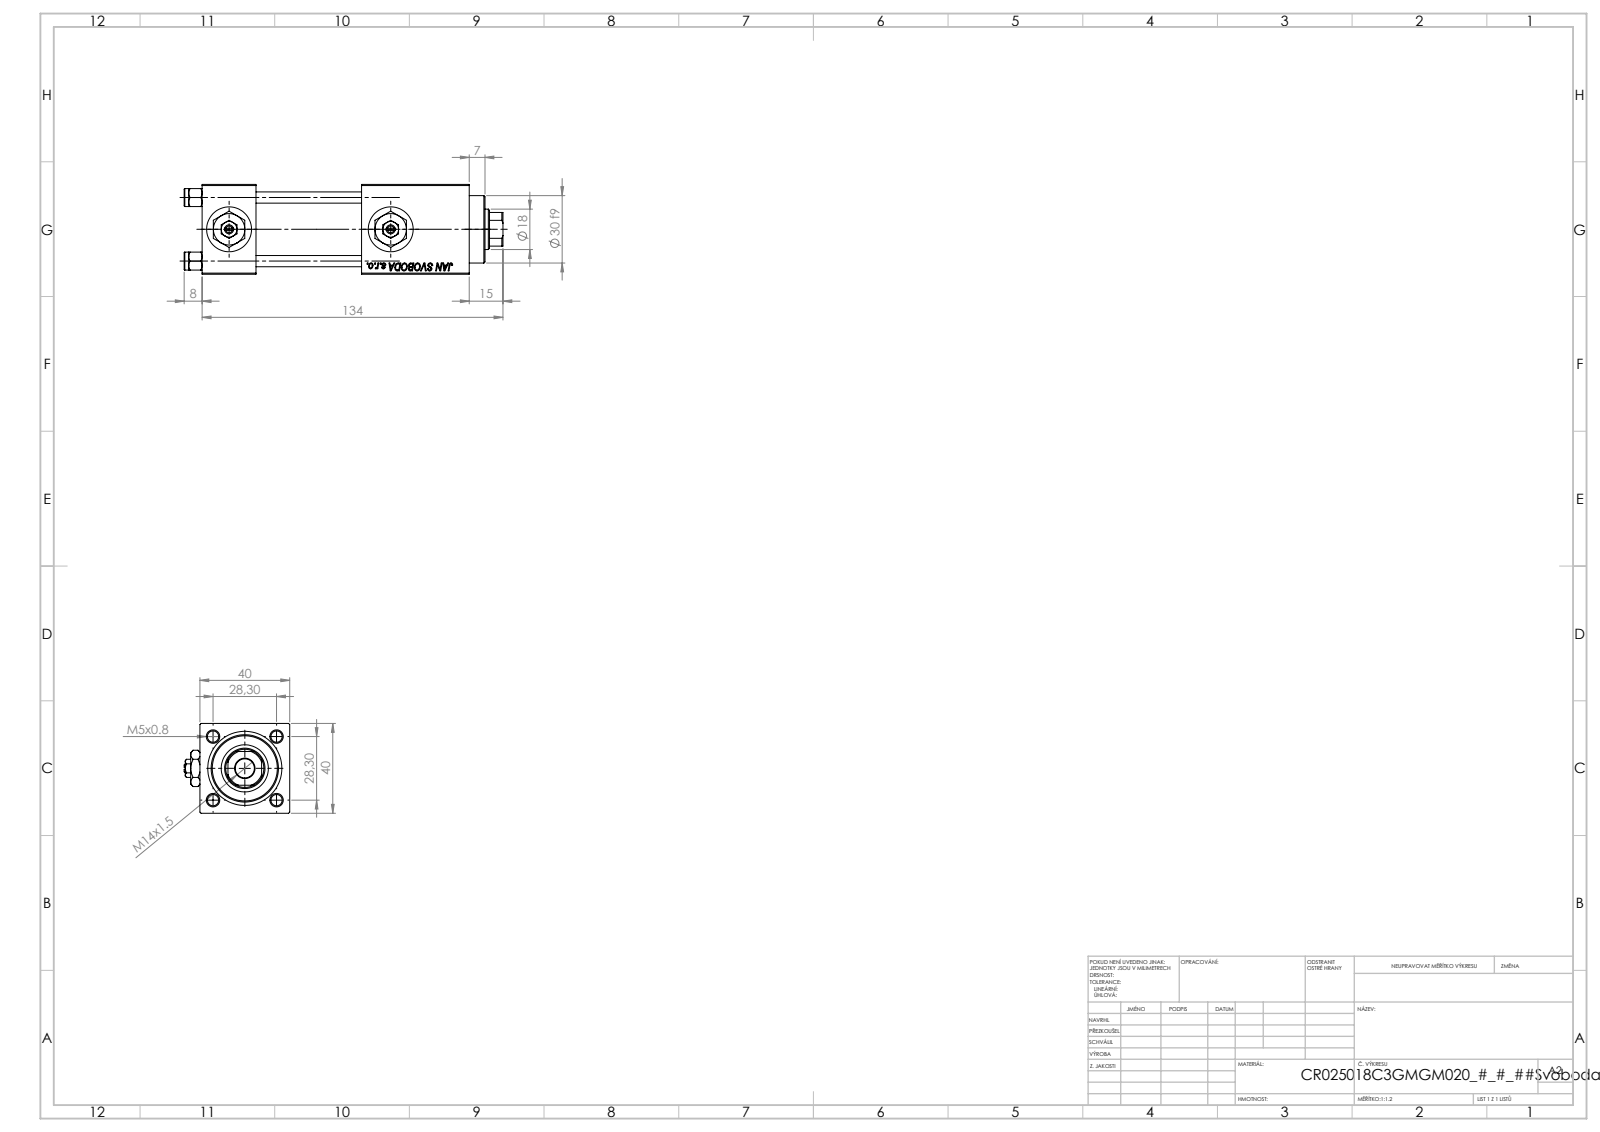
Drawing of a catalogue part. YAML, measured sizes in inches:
part_name: "V215_VC_A; V215CR_C_TYCINKA; NUT_M5_C; Zatka_pro_OIL_PORT (+2 more)"
step_written_by: "SolidWorks 2019 (CONFIG_CONTROL_DESIGN)"
units: inches
bodies: {solids: 13, faces: 1245, planar: 571, cylindrical: 96, other: 578}
overall_size: [5.591, 1.85, 1.575]
volume: 9.068
surface_area: 90.65
round_holes:
  - {diameter: 0.197, count: 4}
  - {diameter: 0.787, count: 3}
  - {diameter: 0.276, count: 2}
  - {diameter: 0.518, count: 2}
  - {diameter: 0.335, count: 1}
  - {diameter: 0.709, count: 1}
  - {diameter: 0.827, count: 1}
  - {diameter: 0.984, count: 1}
  - {diameter: 1.181, count: 1}
round_bosses_or_shafts:
  - {diameter: 0.315, count: 4}
  - {diameter: 1.22, count: 1}
partial_cylinders:
  - {radius: 0.335, count: 1}
face_to_face_distances: [1.575, 0.945, 1.567, 1.85, 2.795, 3.555, 2.61, 0.76, 1.89, 4.685]
hole_center_spacings: [0.788, 1.114, 1.576, 2.835]
